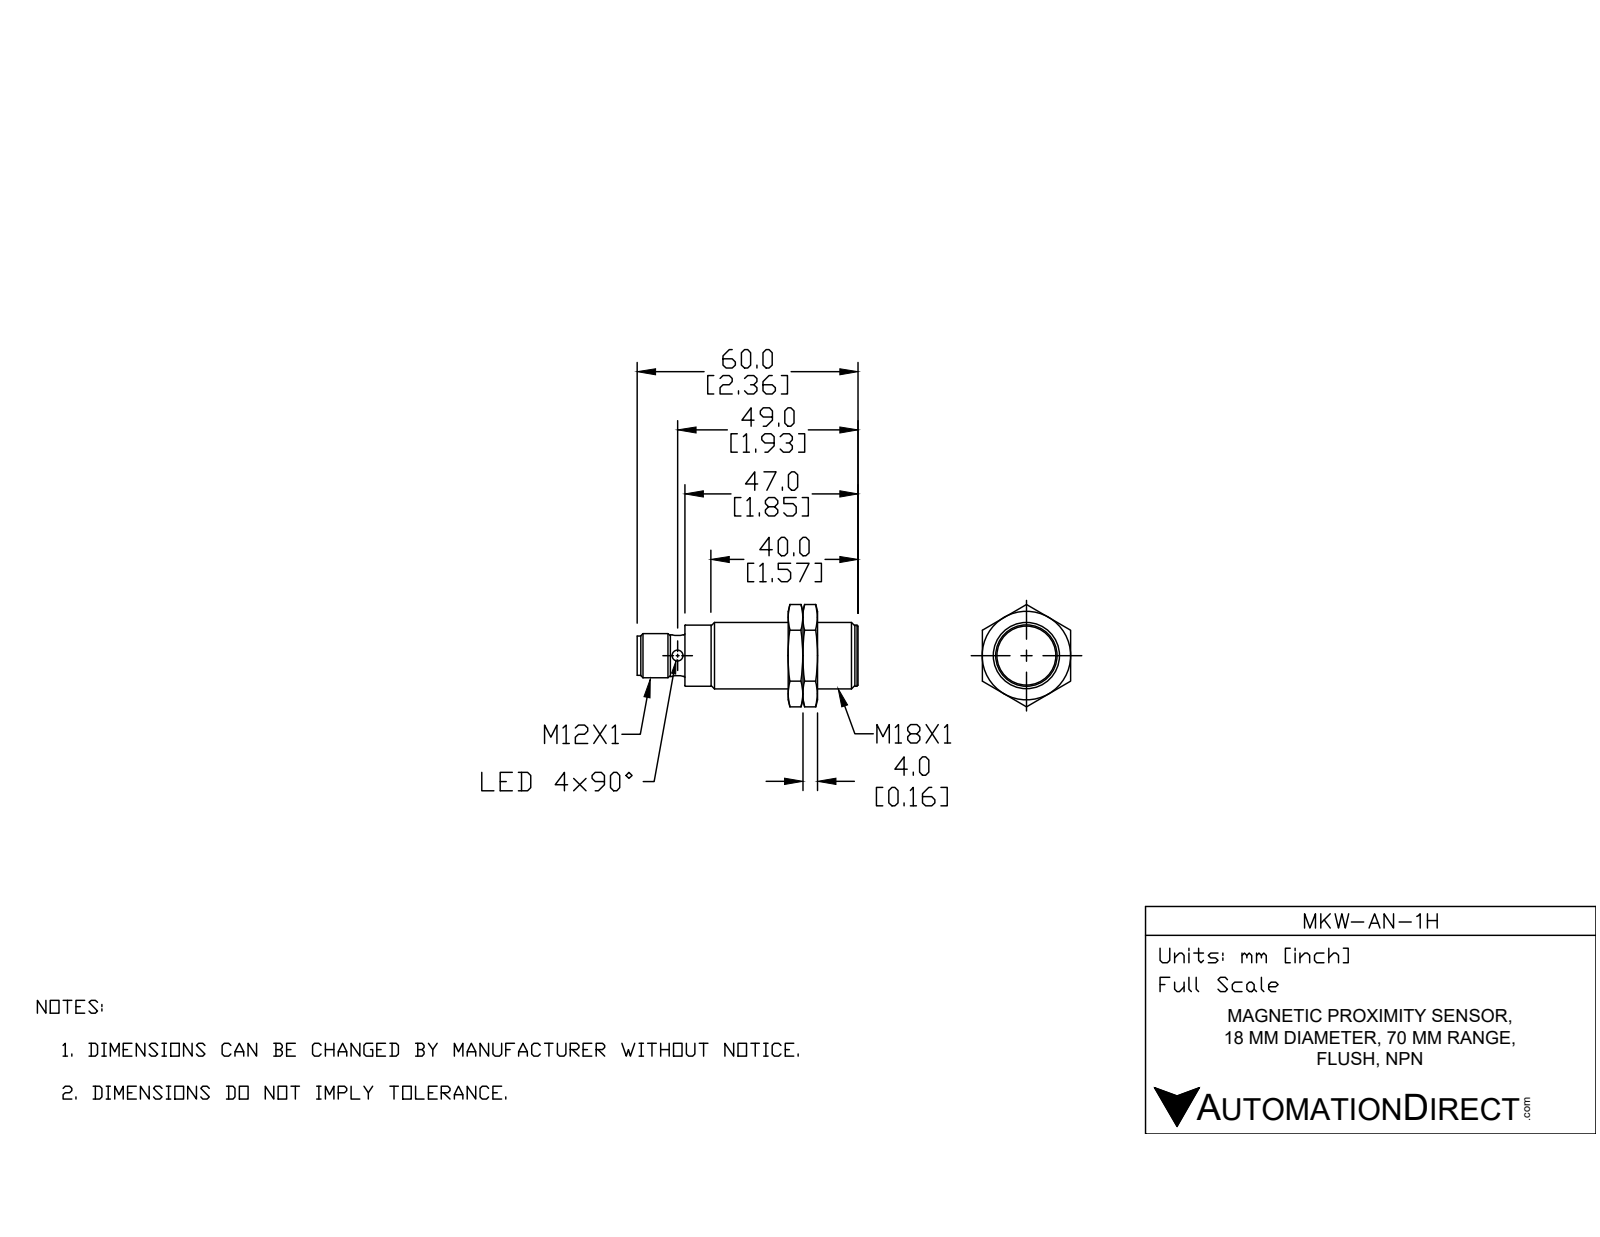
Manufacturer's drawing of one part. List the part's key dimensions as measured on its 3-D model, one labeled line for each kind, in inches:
Part name (STEP PRODUCT): MKW-AP-1H
STEP written by: SolidWorks 2021 (AUTOMOTIVE_DESIGN)
Units: inches
Bodies: 3 solids, 83 faces (28 planar, 19 cylindrical, 36 other)
Overall size (bounding box): 2.362 × 1.091 × 0.945
Volume: 0.892 in³ · Surface area: 9.191 in²
Round holes (diameter × count): ⌀0.118 ×2, ⌀0.331 ×1, ⌀0.666 ×1
Round bosses / shafts (diameter × count): ⌀0.709 ×1, ⌀0.654 ×1, ⌀0.63 ×1, ⌀0.472 ×1, ⌀0.445 ×1, ⌀0.417 ×1
Partial cylindrical surfaces — rounded edges, fillets, slot ends (radius × count): R0.024 ×1, R0.203 ×1
Main face-to-face distances: 0.157, 0.945, 0.591, 0.315, 0.433, 0.748, 1.26, 1.417, 1.102, 1.85
